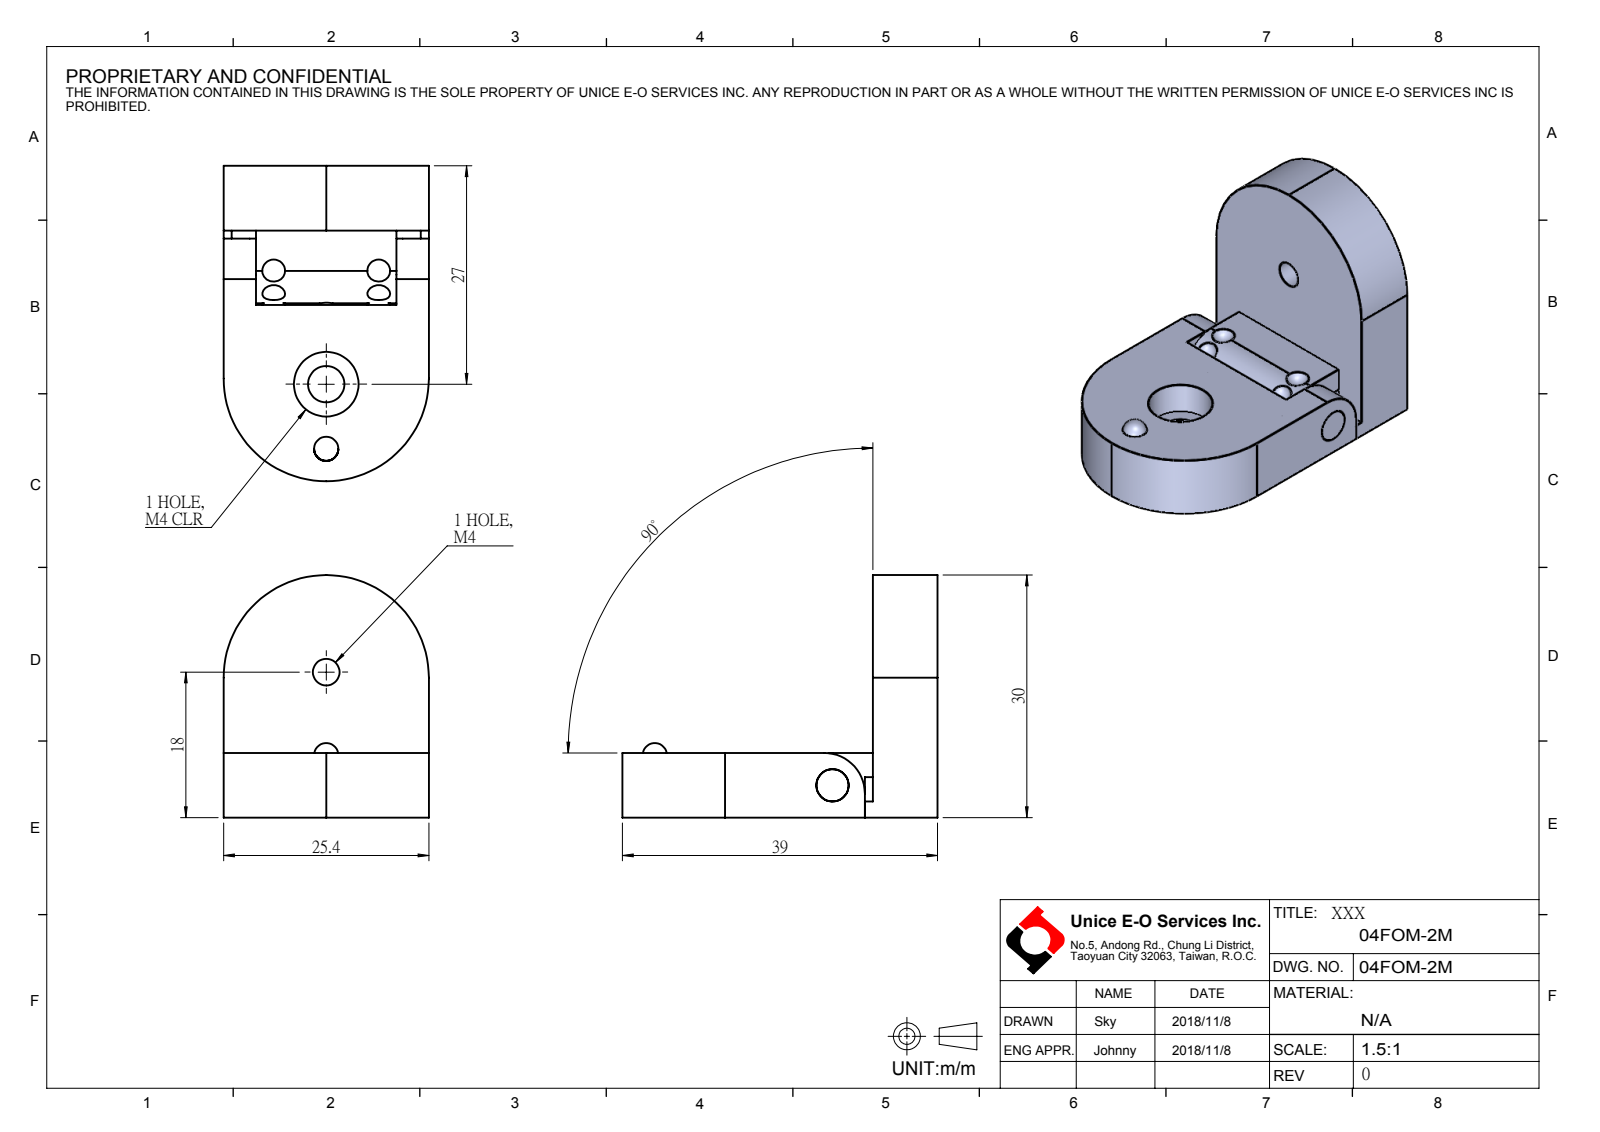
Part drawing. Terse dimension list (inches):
name: 04FOM-2M
written by: SolidWorks 2016 (AUTOMOTIVE_DESIGN)
unit: in
bodies: 0 solids, 52 faces (22 planar, 20 cylindrical, 10 other)
size: 1.535 × 1.181 × 1
holes: 1× ⌀0.13, 1× ⌀0.157, 1× ⌀0.177, 1× ⌀0.315
rounds: 2× R0.118, 2× R0.5, 1× R0.157, 1× R0.197
face distances: 0.315, 1, 0.157, 0.843, 0.677, 0.362, 0.685, 0.354, 0.039, 0.323
